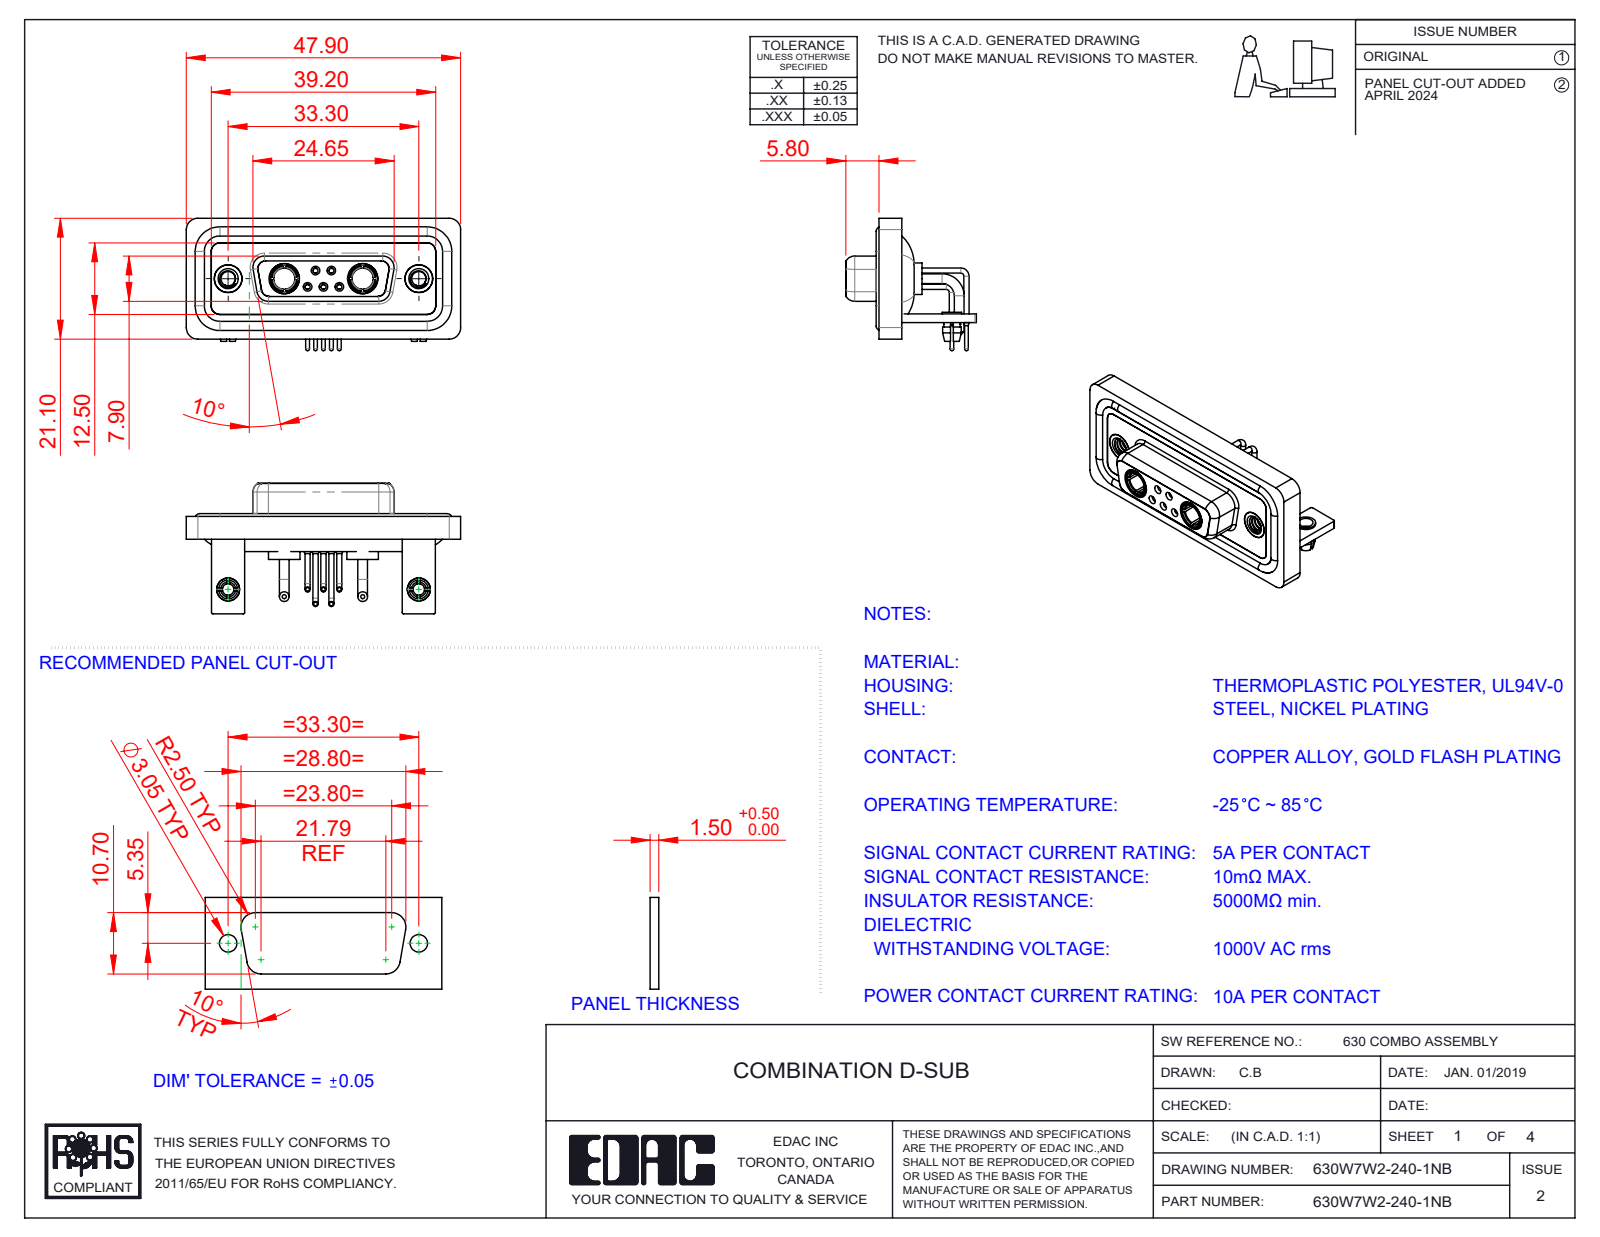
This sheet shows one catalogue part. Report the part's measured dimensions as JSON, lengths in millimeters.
{"part_name": "630Combo Threaded Rivet_A; 630Combo Contact Row 2_50 Contacts; 630Combo Board Lock_50 Contacts; 630Combo Contact Row 1_50 Contacts (+7 more)", "step_written_by": "SolidWorks 2023 (CONFIG_CONTROL_DESIGN)", "units": "millimeters", "bodies": {"solids": 20, "faces": 941, "planar": 306, "cylindrical": 407, "other": 228}, "overall_size": [47.9, 23.12, 22.8], "volume_mm3": 6476, "surface_area_mm2": 11053, "round_holes": [[2, 7], [0.9, 5], [1.1, 5], [1.5, 5], [2.5, 4], [4.85, 4], [1.6, 3], [1.7, 2], [3.2, 2], [3.7, 2], [4, 2], [4.05, 2]], "round_bosses_or_shafts": [[1.6, 6], [0.9, 5], [0.65, 5], [1.7, 4], [5.5, 2], [5.2, 2], [4.96, 2], [4.95, 2]], "partial_cylinders_radius": [[2, 21], [1.5, 18], [0.25, 16], [1.35, 12], [1.6, 8], [0.5, 5], [0.6, 4], [0.65, 4]], "face_to_face_distances": [0.4, 2.9, 1.5, 1.8, 3.7, 1.1, 4.1, 1.6, 2.5, 1.4], "hole_center_spacings": [3.16, 2.77, 9.8, 23.5, 33.3, 4.31, 4.33, 5.03]}
